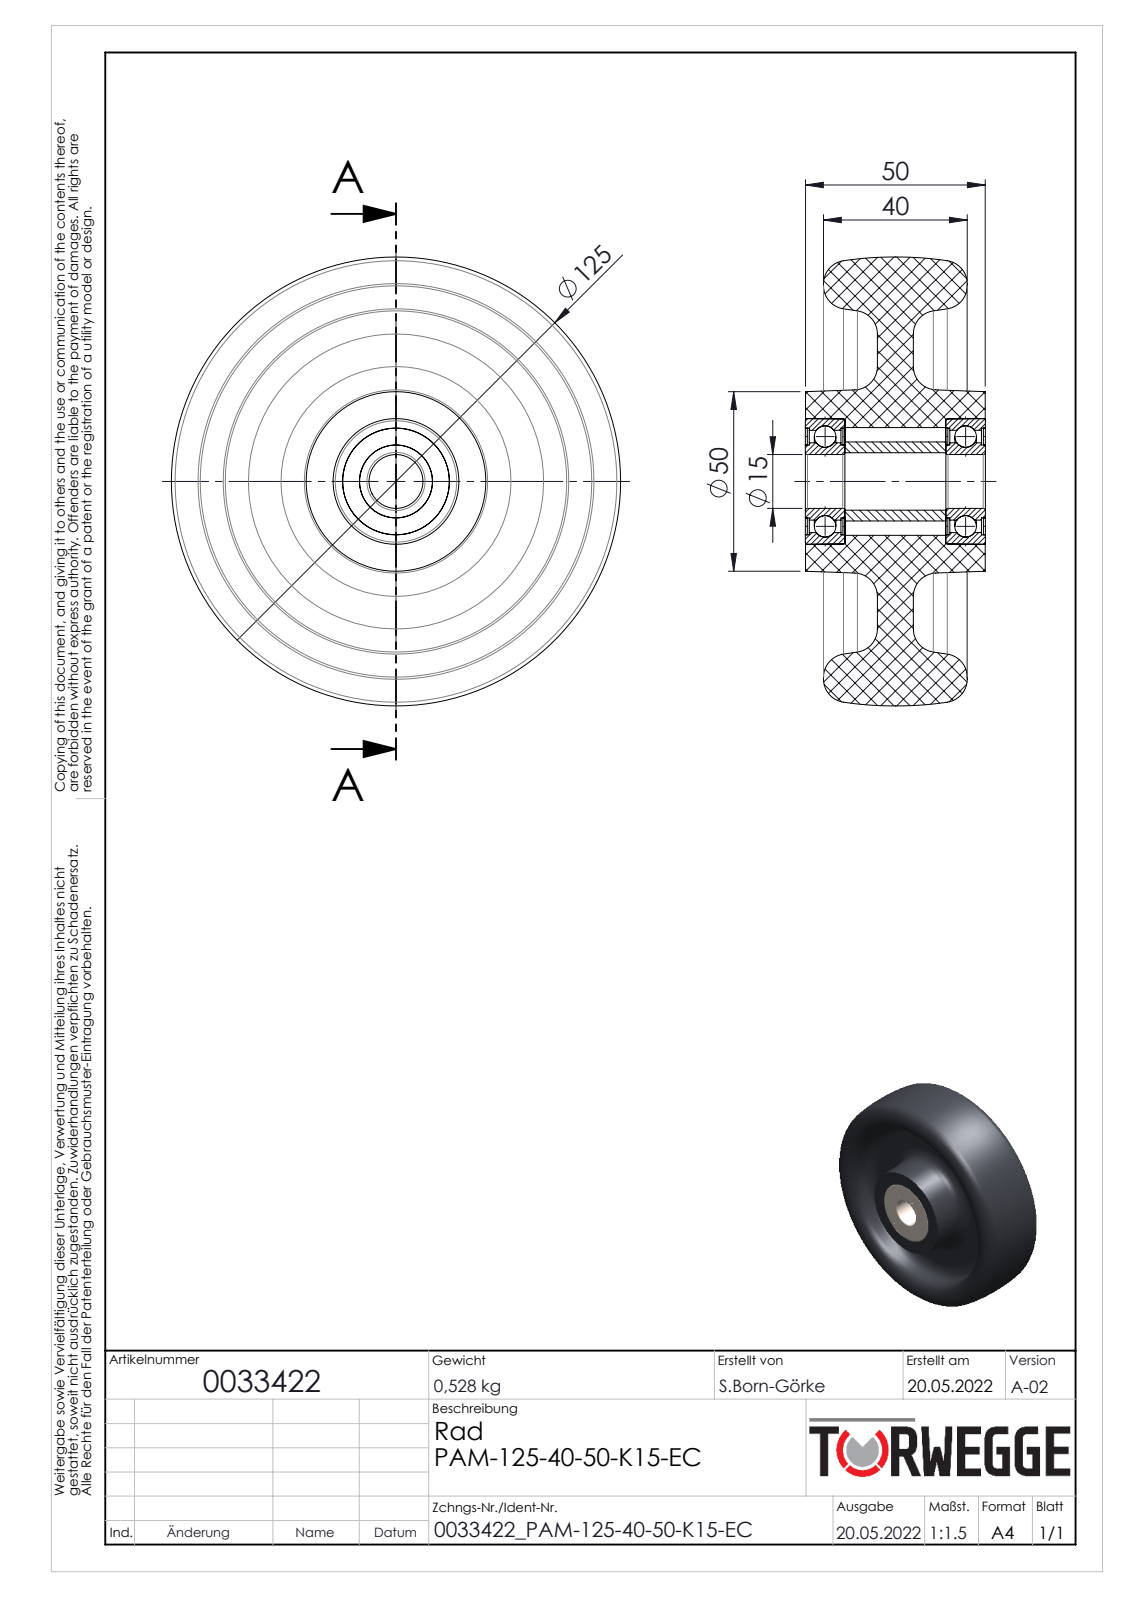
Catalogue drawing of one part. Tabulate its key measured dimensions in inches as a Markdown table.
| quantity | value |
| --- | --- |
| part name | 0033422 |
| STEP written by | SolidWorks 2020 (AUTOMOTIVE_DESIGN) |
| units | inches |
| bodies | 12 solids, 166 faces (32 planar, 62 cylindrical, 72 other) |
| overall size | 4.921 × 4.921 × 1.972 |
| volume | 19.72 in³ |
| surface area | 109.4 in² |
| round holes (diameter × count) | 0.591 × 1, 0.63 × 1, 0.799 × 1, 1.121 × 1, 1.169 × 1, 1.181 × 1 |
| round bosses / shafts (diameter × count) | 1.378 × 1, 0.866 × 1, 0.847 × 1 |
| main face-to-face distances | 1.539, 1.537, 0.394, 0.787, 1.181, 0.022, 0.433, 0.431, 0.356, 0.75 |
